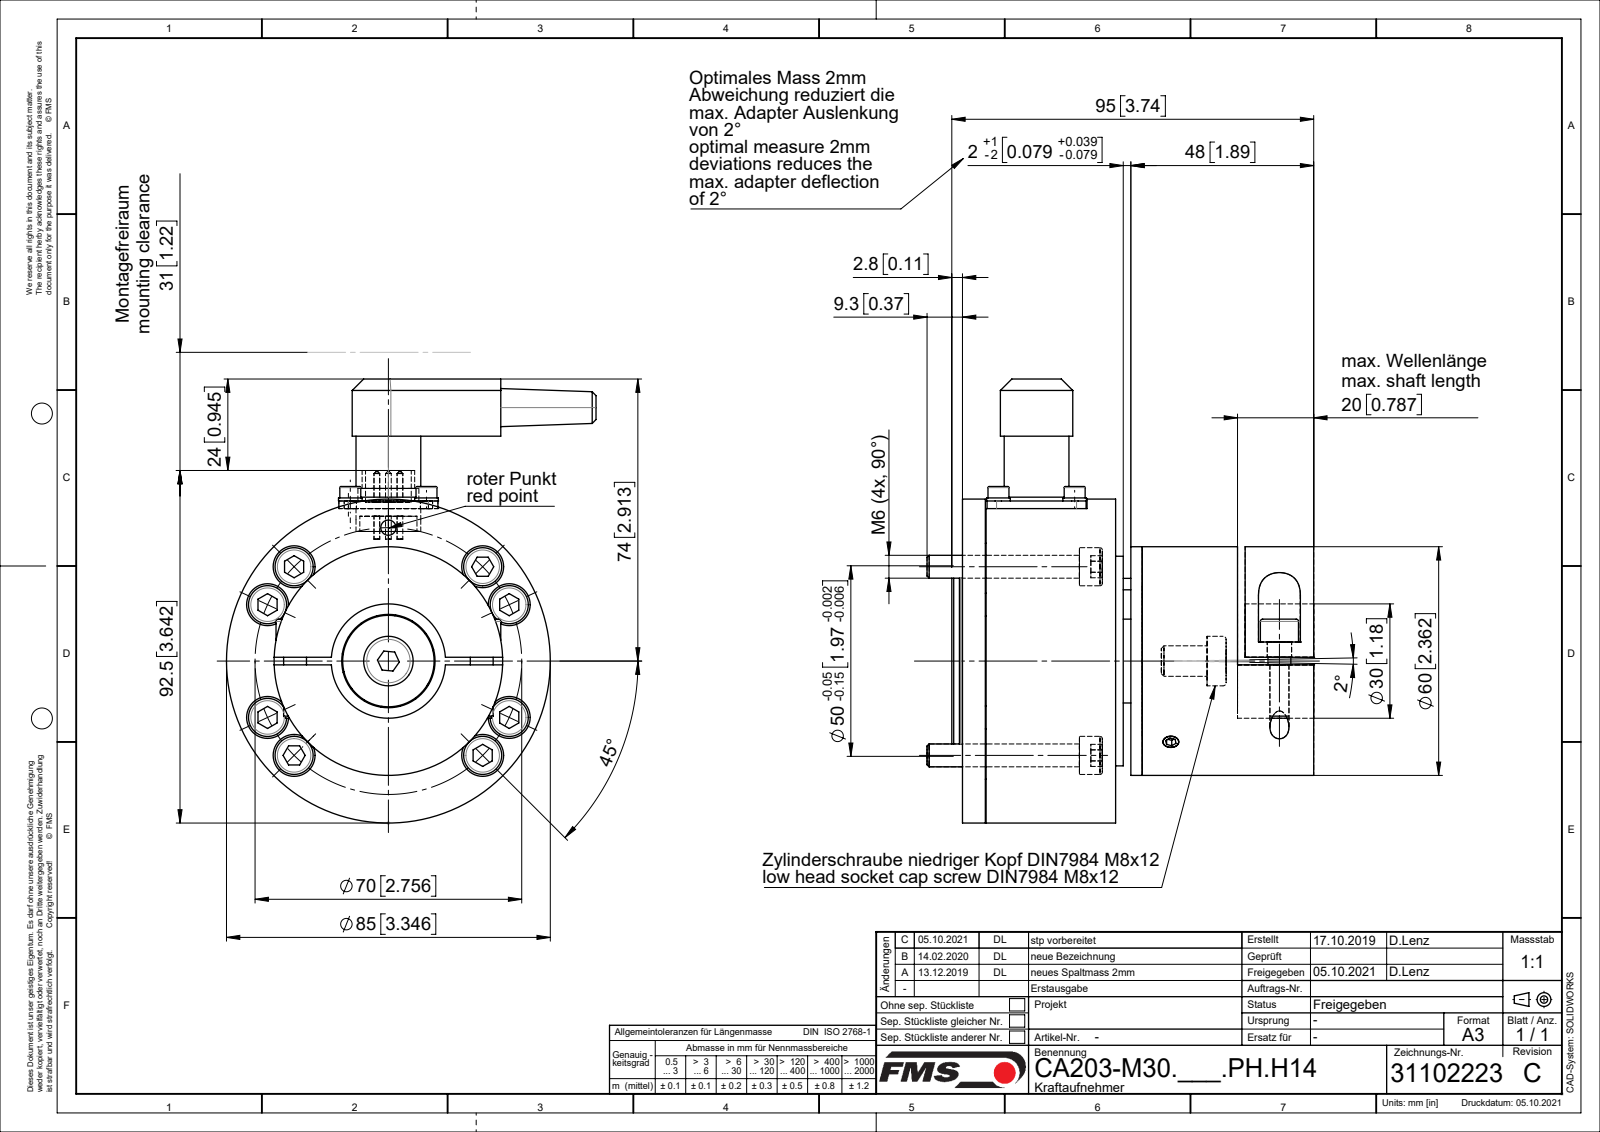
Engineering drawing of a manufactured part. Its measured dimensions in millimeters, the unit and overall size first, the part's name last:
Units: millimetres
Overall size (bounding box): 116.5 × 101.5 × 97
Round holes (diameter × count): ⌀2.5 ×8, ⌀6.5 ×8, ⌀11 ×8, ⌀5 ×6, ⌀2 ×5, ⌀4 ×5, ⌀3.1 ×4, ⌀3.2 ×4, ⌀3.6 ×4, ⌀7 ×4, ⌀6.4 ×2, ⌀3 ×1
Round bosses / shafts (diameter × count): ⌀6 ×11, ⌀10 ×10, ⌀3 ×8, ⌀1.5 ×5, ⌀6.2 ×4, ⌀5.7 ×4, ⌀5.5 ×4, ⌀85 ×1
Partial cylindrical surfaces — rounded edges, fillets, slot ends (radius × count): R2.5 ×4, R5 ×2, R5.5 ×2, R9.5 ×1
Main face-to-face distances: 2, 41, 30, 6, 45, 10, 34, 3, 50, 15
Hole centre spacings: 35, 20, 24.78, 25.2, 32.8, 51.14, 56.46, 6
Volume: 301 285 mm³ · Surface area: 111 790 mm²
Bodies: 44 solids, 839 faces (302 planar, 339 cylindrical, 198 other)
Part name (STEP PRODUCT): Gew-Sti-I6kt-Zapfen DIN915_M5x10; 090409-3_01; Zyl-Schr DIN912_M6x30; 070907-2_01 (+8 more)
STEP written by: SolidWorks 2018 (CONFIG_CONTROL_DESIGN)
